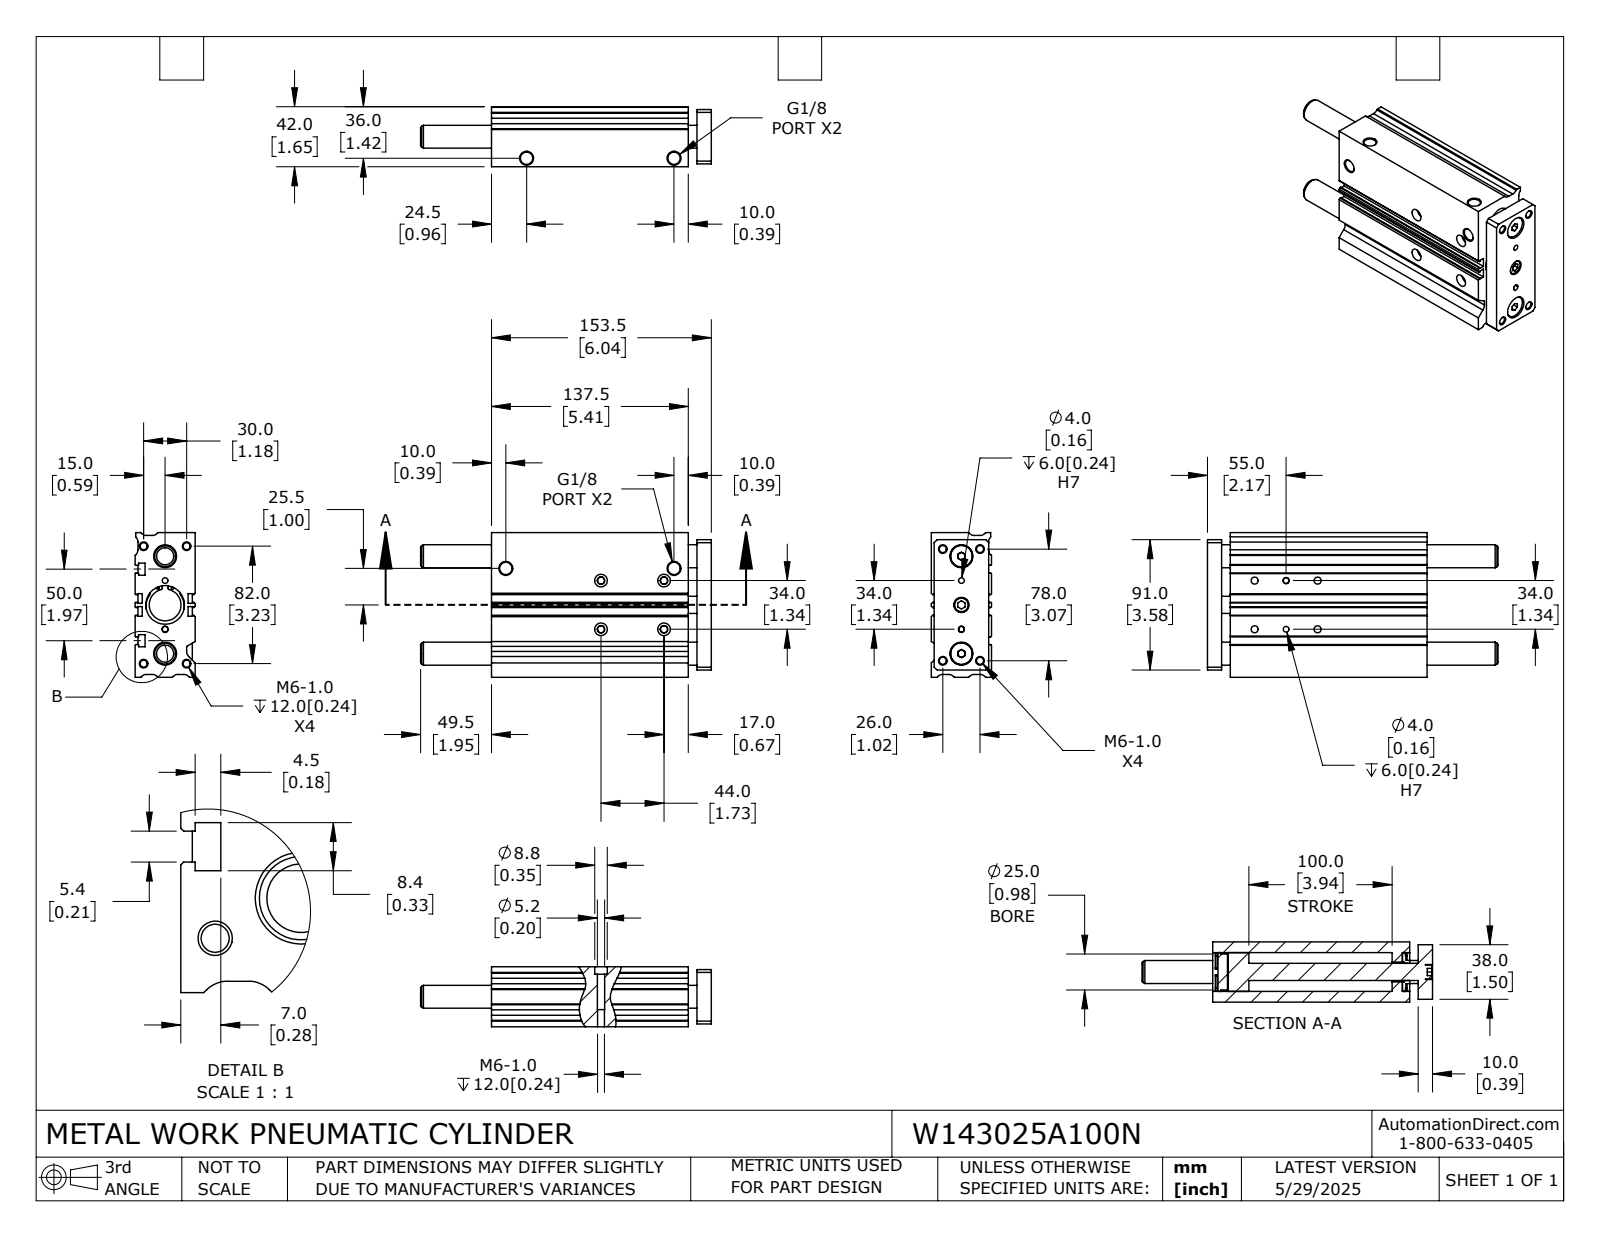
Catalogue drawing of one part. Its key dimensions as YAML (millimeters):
part_name: "W143025A100N_ROD; W143025A100N_BODY; W143025A100N"
step_written_by: "SolidWorks 2024 (CONFIG_CONTROL_DESIGN)"
units: millimeters
bodies: {solids: 6, faces: 390, planar: 191, cylindrical: 157, other: 42}
overall_size: [203, 101, 42]
volume: 531400
surface_area: 130700
round_holes:
  - {diameter: 4.9, count: 8}
  - {diameter: 1.7, count: 4}
  - {diameter: 4, count: 4}
  - {diameter: 4.9, count: 4}
  - {diameter: 5.2, count: 4}
  - {diameter: 8.6, count: 4}
  - {diameter: 8.8, count: 4}
  - {diameter: 16, count: 2}
  - {diameter: 10.5, count: 1}
  - {diameter: 12, count: 1}
  - {diameter: 13.7, count: 1}
  - {diameter: 22.2, count: 1}
round_bosses_or_shafts:
  - {diameter: 15.5, count: 2}
  - {diameter: 27, count: 1}
  - {diameter: 25, count: 1}
  - {diameter: 16.5, count: 1}
  - {diameter: 10, count: 1}
partial_cylinders:
  - {radius: 1, count: 12}
  - {radius: 5, count: 9}
  - {radius: 2, count: 8}
  - {radius: 13.3, count: 2}
  - {radius: 14.2, count: 1}
face_to_face_distances: [42, 5, 2, 35, 37, 3, 6, 16, 10, 153.5]
hole_center_spacings: [34, 2.8, 7.4, 12.7, 13.9, 16.6, 17, 22]
